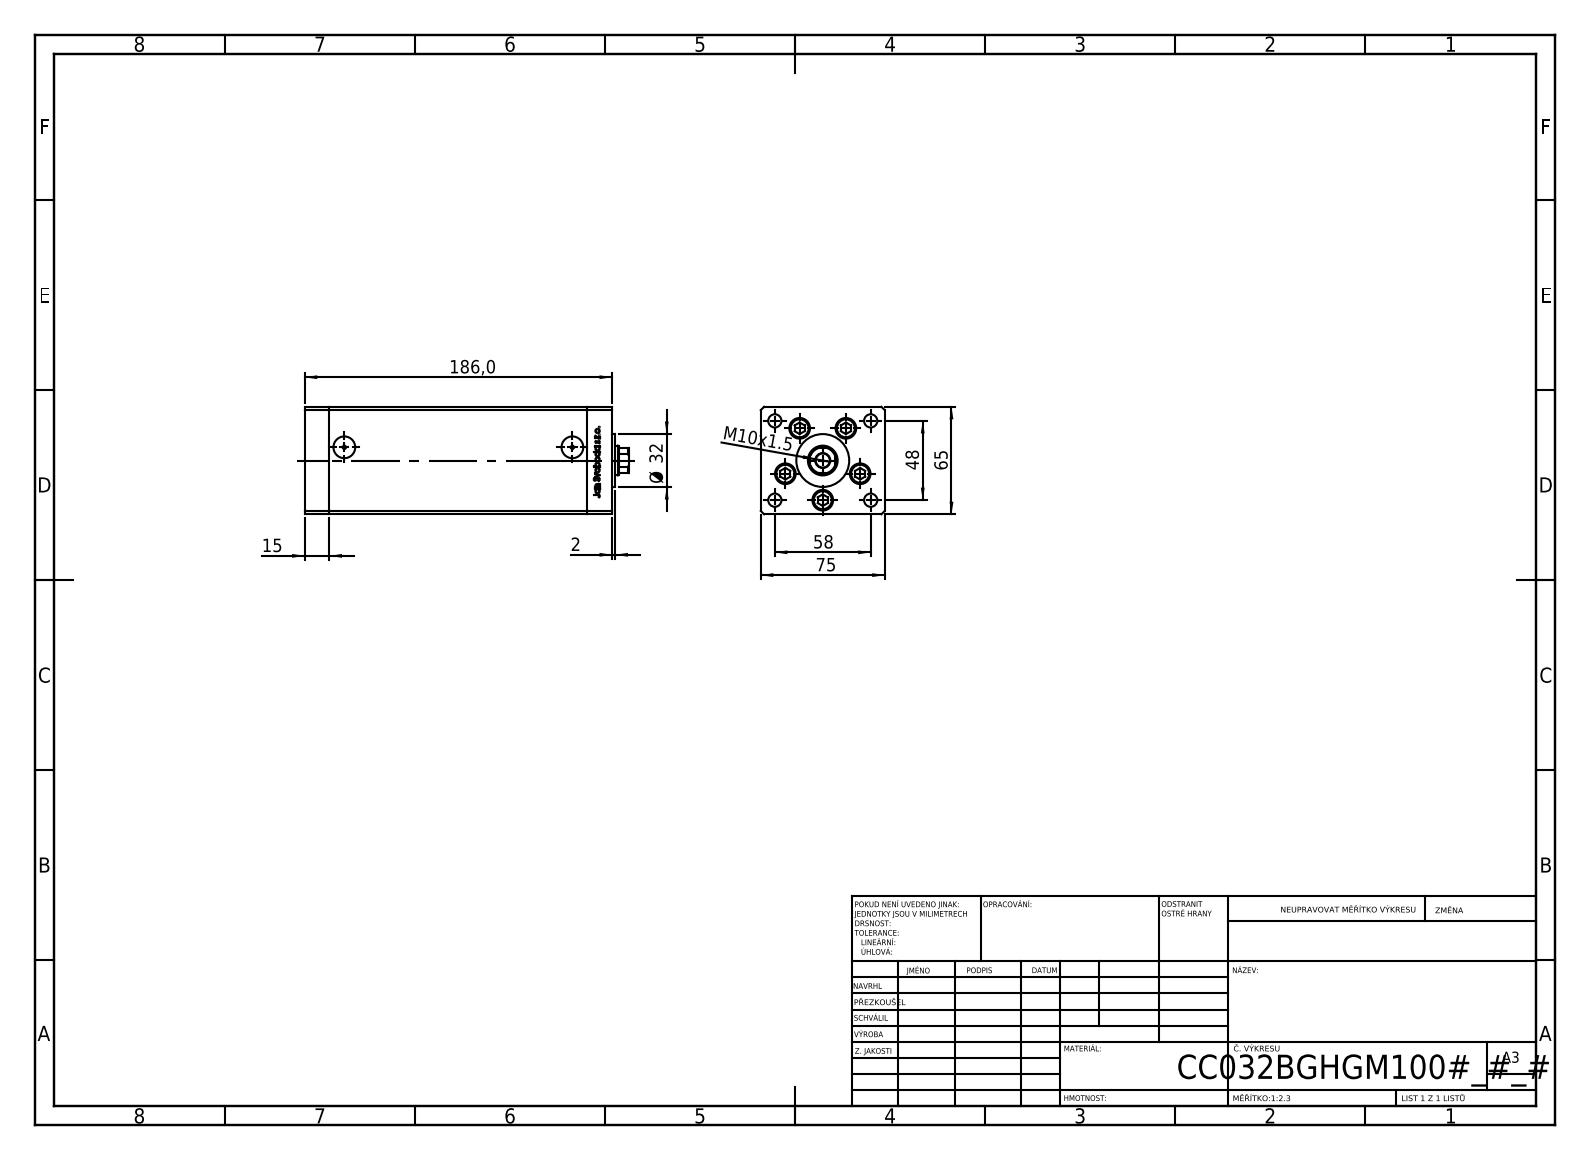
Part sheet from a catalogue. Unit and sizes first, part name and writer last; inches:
Units: inches
Overall size (bounding box): 7.717 × 2.953 × 2.559
Round holes (diameter × count): ⌀0.354 ×5, ⌀0.492 ×5, ⌀0.315 ×4, ⌀0.079 ×2, ⌀0.518 ×2, ⌀0.335 ×1, ⌀0.709 ×1
Round bosses / shafts (diameter × count): ⌀0.315 ×5, ⌀1.26 ×1
Partial cylindrical surfaces — rounded edges, fillets, slot ends (radius × count): R0.037 ×2, R0.335 ×1
Main face-to-face distances: 2.953, 2.559, 0.591, 6.142, 6.732, 7.323, 1.102, 2.146, 0.413, 1.033
Hole centre spacings: 0.945, 1.482, 0.617, 0.678, 1.091, 1.135, 1.142, 1.285
Volume: 49.12 in³ · Surface area: 211.6 in²
Bodies: 14 solids, 1183 faces (462 planar, 147 cylindrical, 574 other)
Part name (STEP PRODUCT): V220C_VC_B; ALLEN BOLT; V220C_FRONT_B; V220C BACK_B (+1 more)
STEP written by: SolidWorks 2019 (CONFIG_CONTROL_DESIGN)
